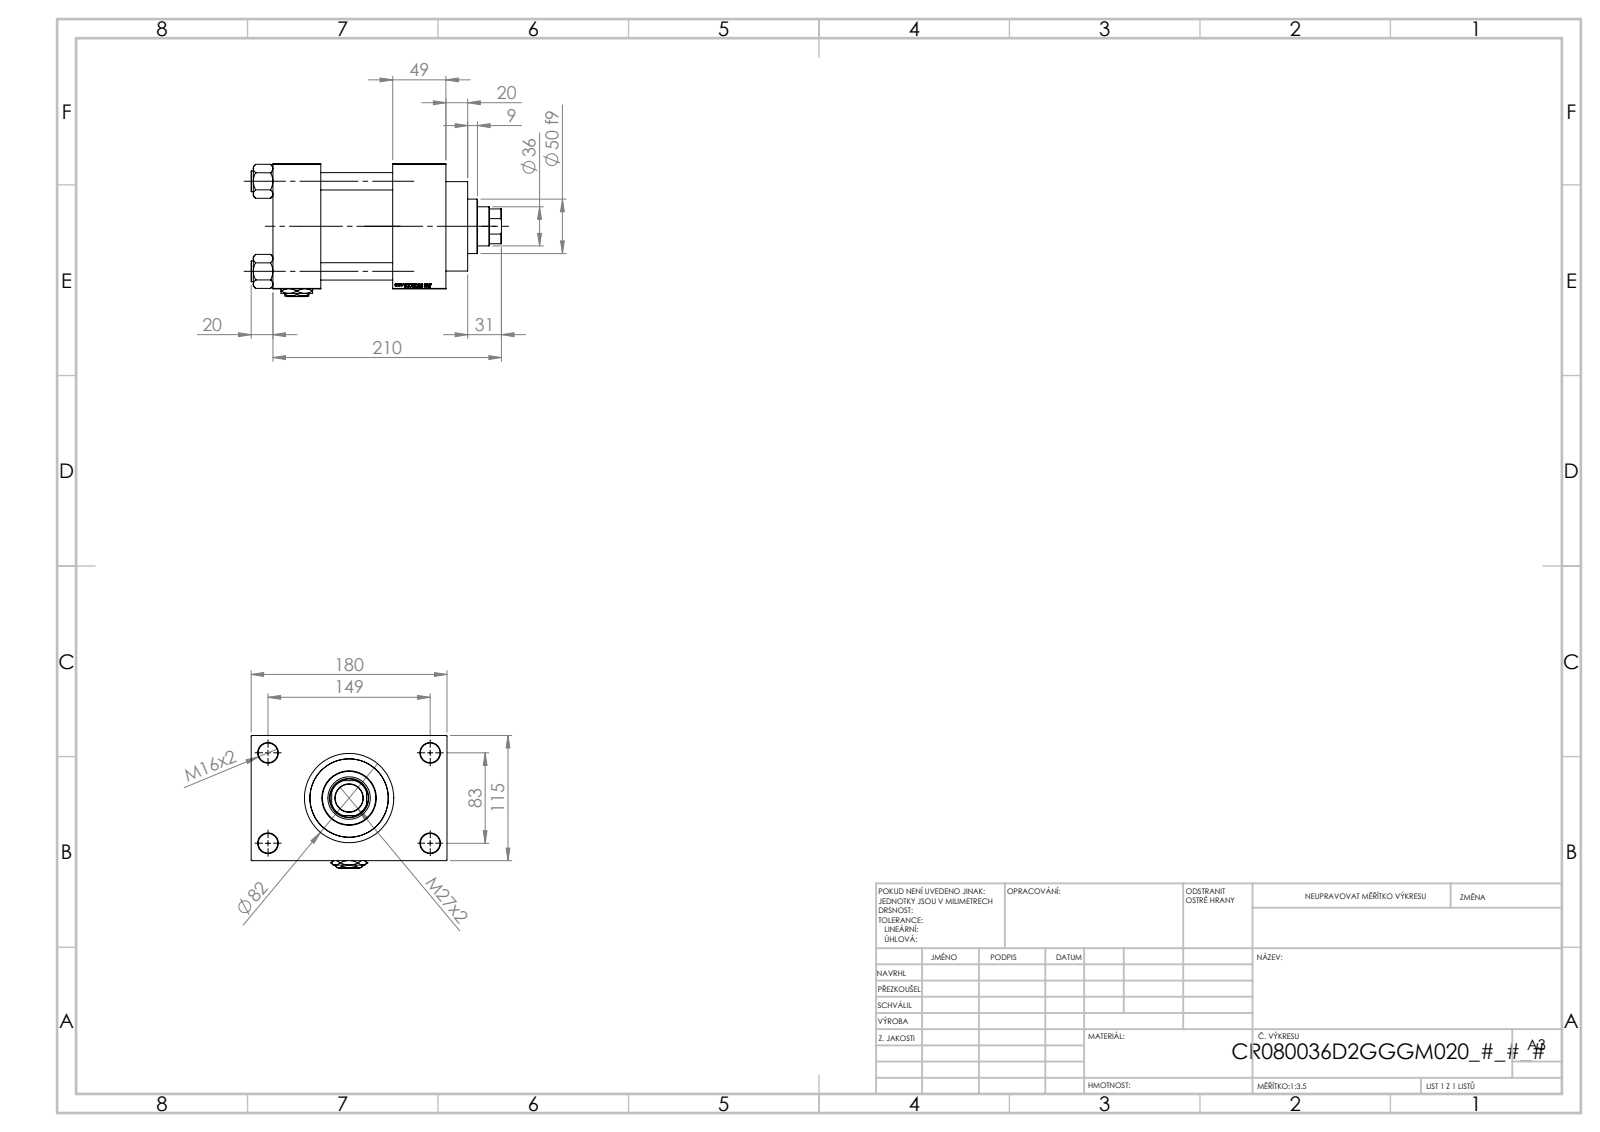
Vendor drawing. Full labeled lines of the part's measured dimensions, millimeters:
Part name (STEP PRODUCT): NUT_M5_D; Zatka_pro_OIL_PORT; V215CR_D_Body; V215CR_D_TYCINKA (+2 more)
STEP written by: SolidWorks 2019 (CONFIG_CONTROL_DESIGN)
Units: millimetres
Bodies: 12 solids, 1205 faces (569 planar, 96 cylindrical, 540 other)
Overall size (bounding box): 230 × 180 × 122
Volume: 1 993 000 mm³ · Surface area: 297 690 mm²
Round holes (diameter × count): ⌀16 ×4, ⌀18 ×4, ⌀7 ×2, ⌀26.44 ×2, ⌀35 ×2, ⌀25.5 ×1, ⌀36 ×1, ⌀39 ×1, ⌀61 ×1, ⌀72 ×1, ⌀80 ×1
Round bosses / shafts (diameter × count): ⌀19 ×4, ⌀86 ×1, ⌀82 ×1, ⌀50 ×1
Partial cylindrical surfaces — rounded edges, fillets, slot ends (radius × count): R17.5 ×1
Main face-to-face distances: 115, 66, 110, 49, 44, 159, 32.5, 147.5, 20, 69
Hole centre spacings: 33.15, 58.48, 82.7, 85.28, 89.24, 115.85, 142.43, 83
